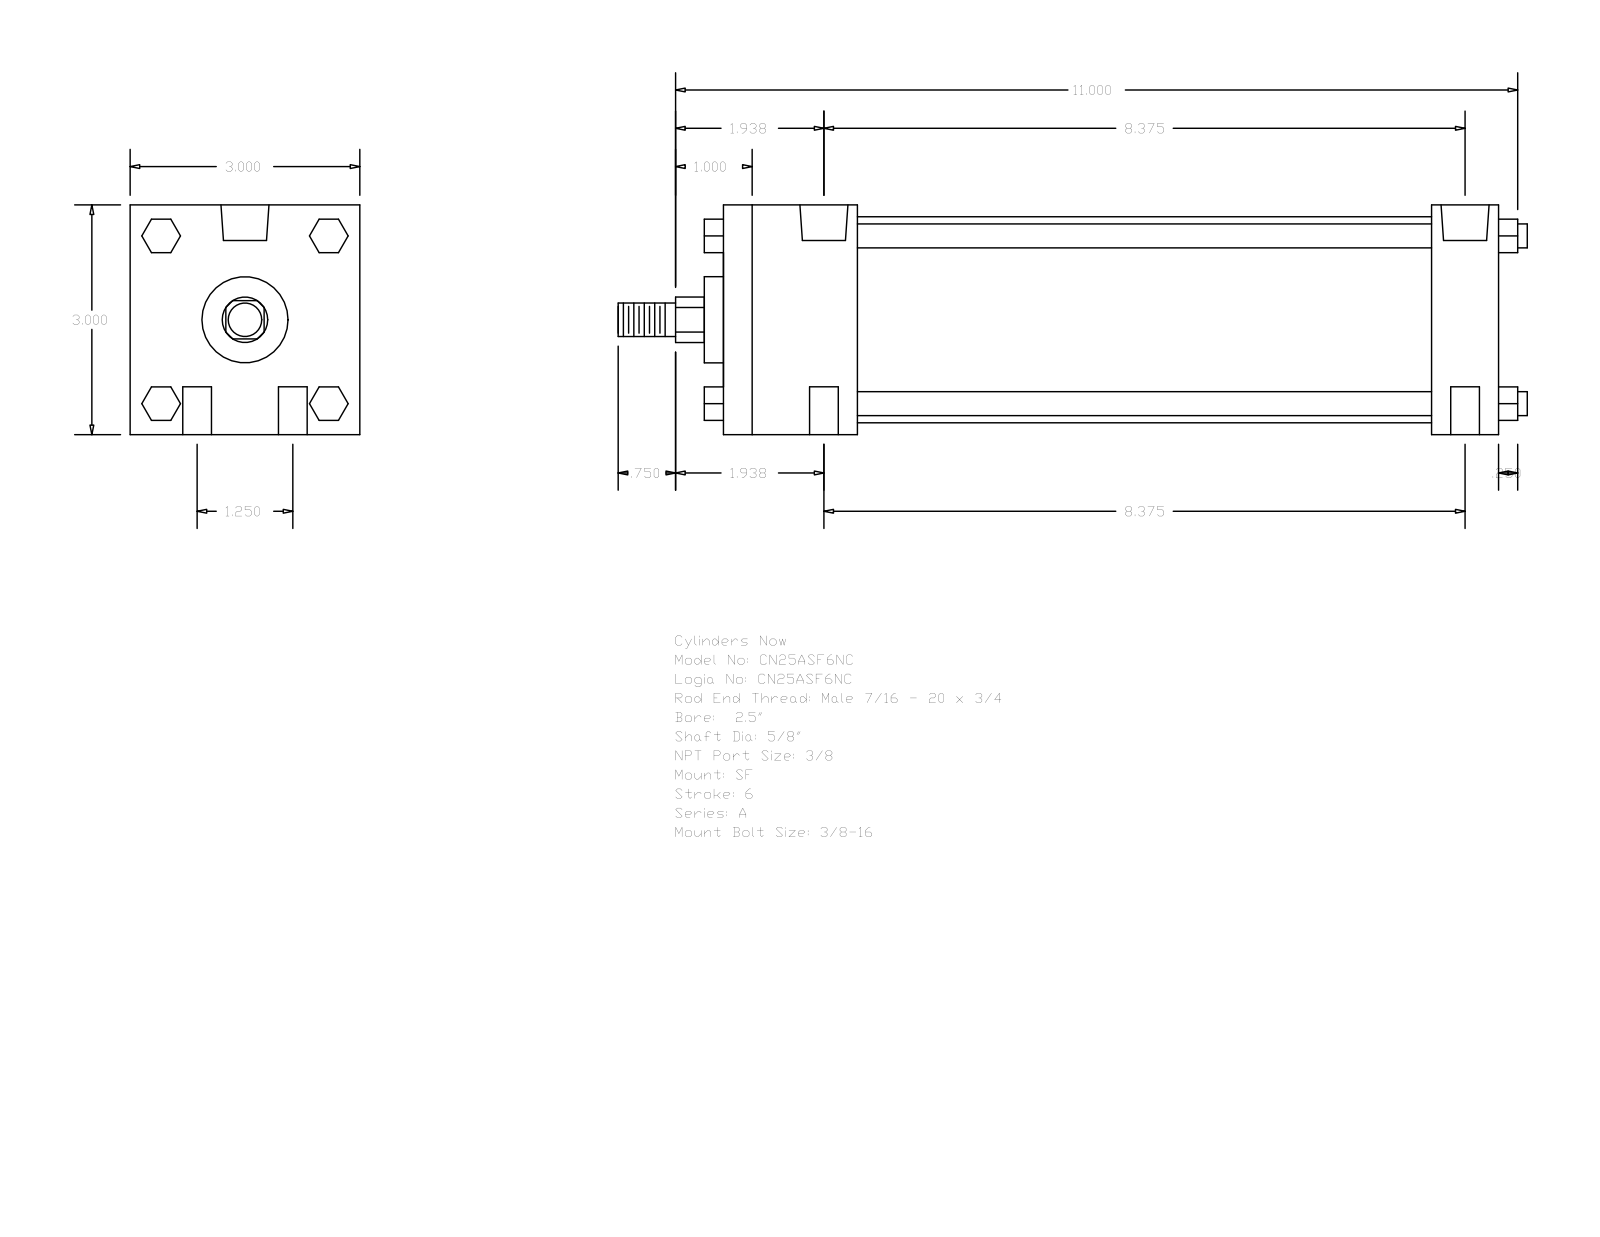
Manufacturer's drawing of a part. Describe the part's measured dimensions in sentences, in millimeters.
The part is named "A_SF__0250_0.625". Its 3-D file was written by "GSSL Pune (CONFIG_CONTROL_DESIGN)". It is 0 solids with 124 faces: 94 planar, 30 cylindrical and 0 other. Overall it measures 301.62 by 76.2 by 76.2 millimeters. Round holes: 4 of diameter 9.53, 2 of diameter 5.56, 2 of diameter 15.93. Round bosses or shafts: 4 of diameter 7.94, 1 of diameter 68.33, 1 of diameter 28.57, 1 of diameter 15.88, 1 of diameter 11.11. Partial cylindrical surfaces (rounded edges, fillets, slot ends): 1 of radius 7.54. The main face-to-face distances are 76.2, 257.17, 44.45, 234.94, 22.23, 190.49, 212.72, 6.35, 263.52, 50.8. The hole center spacings are 15.88, 213.32, 212.73, 31.76, 215.09, 217.49.
